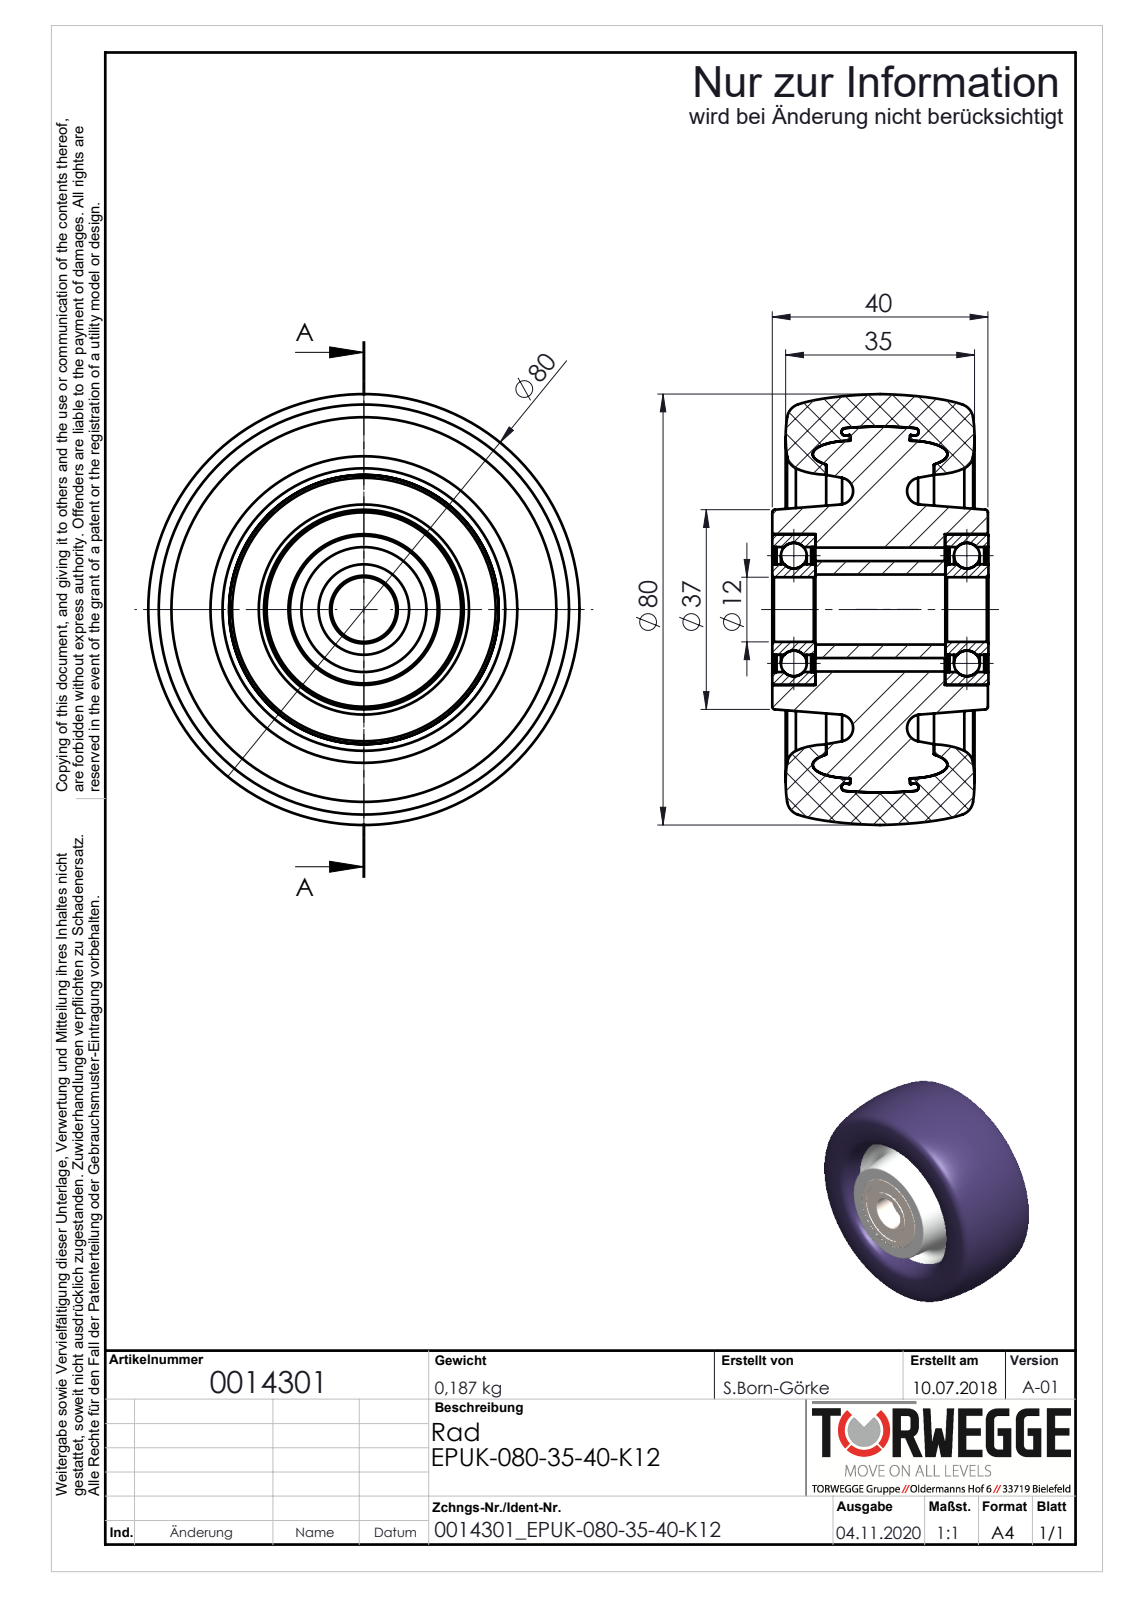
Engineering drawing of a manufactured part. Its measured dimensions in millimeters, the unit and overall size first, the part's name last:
Units: millimetres
Overall size (bounding box): 80 × 80 × 40.1
Round holes (diameter × count): ⌀12 ×1, ⌀13 ×1, ⌀16.8 ×1, ⌀23 ×1, ⌀23.2 ×1, ⌀28 ×1
Round bosses / shafts (diameter × count): ⌀18 ×1
Partial cylindrical surfaces — rounded edges, fillets, slot ends (radius × count): R31.4 ×1
Main face-to-face distances: 32.1, 8, 0.8, 0.5, 7.2, 7.7, 6.9, 32, 40, 32.4
Volume: 141 433 mm³ · Surface area: 38 395 mm²
Bodies: 12 solids, 249 faces (36 planar, 57 cylindrical, 156 other)
Part name (STEP PRODUCT): 0014301
STEP written by: SolidWorks 2018 (AUTOMOTIVE_DESIGN)
